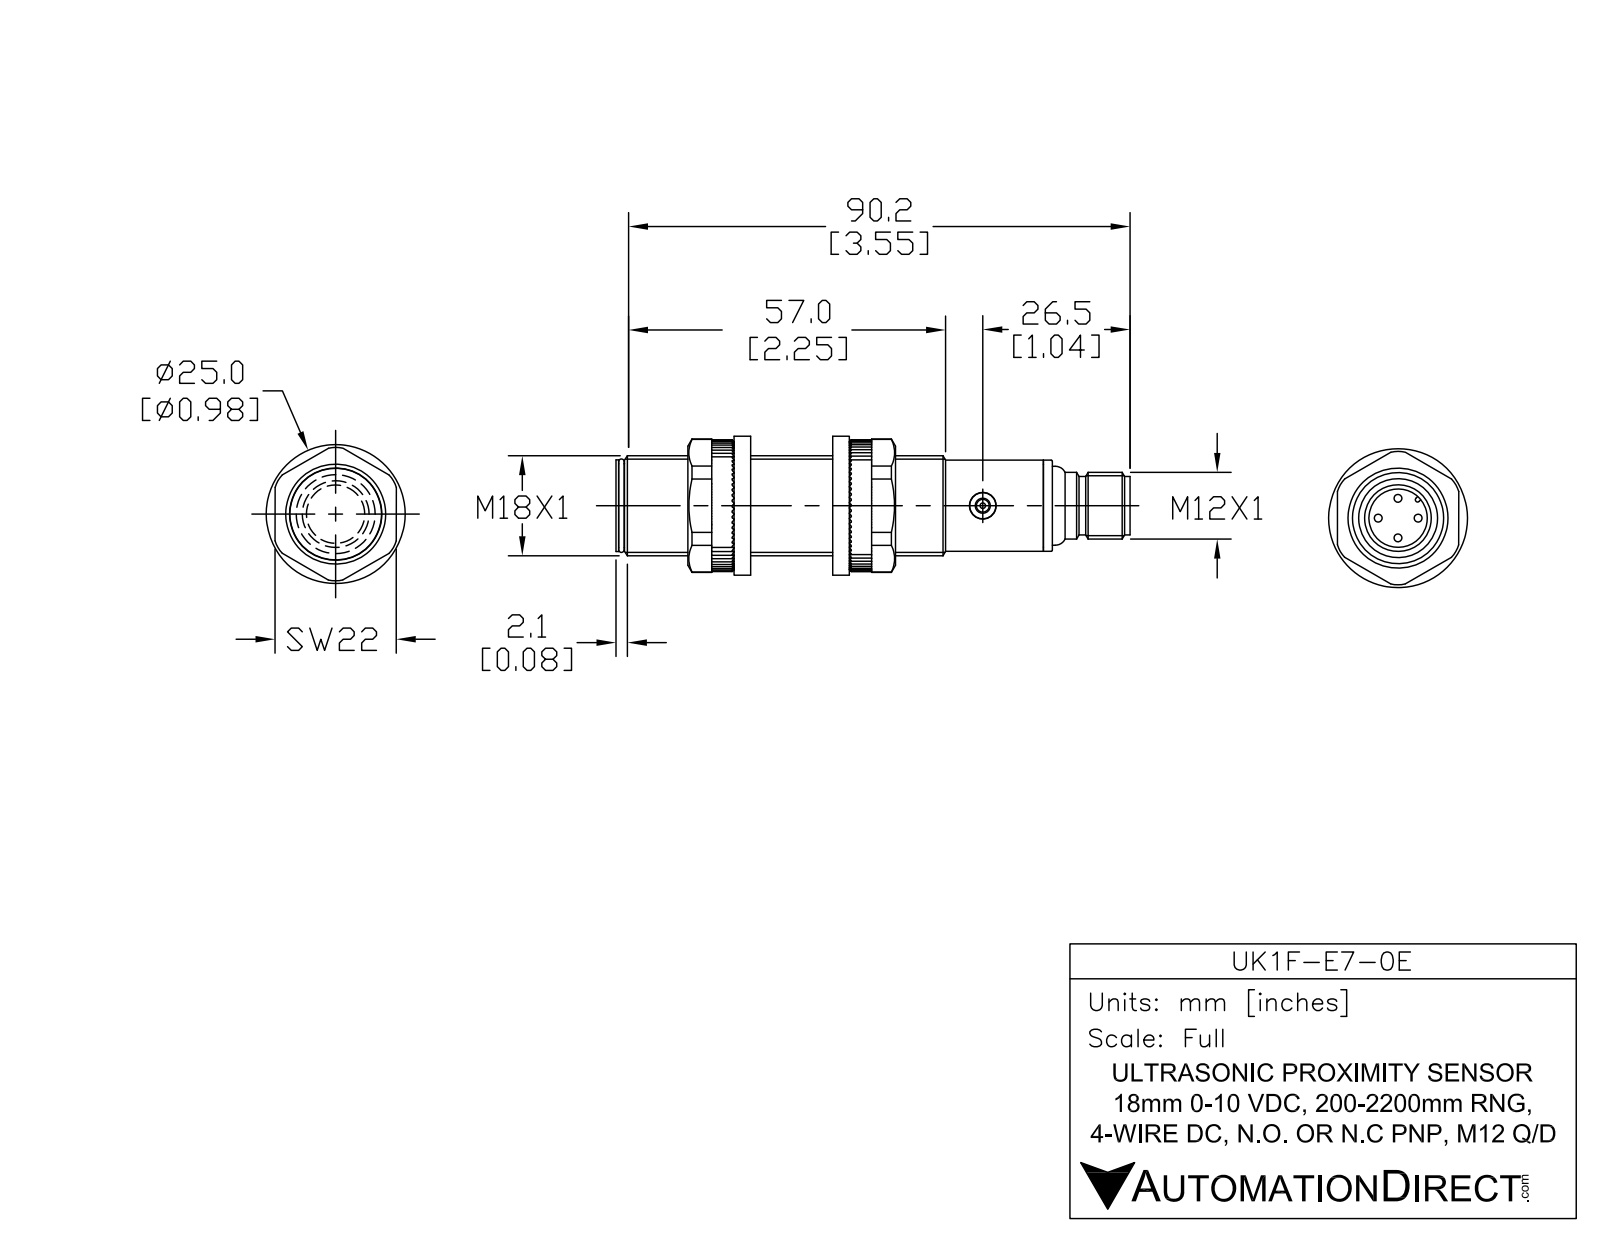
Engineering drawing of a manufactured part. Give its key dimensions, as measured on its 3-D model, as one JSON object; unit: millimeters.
{"part_name": "UK1F-E7-0E", "step_written_by": "SolidWorks 2017 (AUTOMOTIVE_DESIGN)", "units": "millimeters", "bodies": {"solids": 6, "faces": 106, "planar": 21, "cylindrical": 48, "other": 37}, "overall_size": [91.6, 18, 18], "volume_mm3": 19700, "surface_area_mm2": 6890, "round_holes": [[2.7, 1], [4.7, 1], [7, 1], [8.3, 1], [9.5, 1]], "round_bosses_or_shafts": [[1, 4], [18, 1], [16.6, 1], [16.4, 1], [15.8, 1], [14.2, 1], [12, 1], [10.5, 1]], "partial_cylinders_radius": [[0.6, 1]], "face_to_face_distances": [75.1, 1, 76.1, 0.9, 76, 1.1, 4, 77.6, 77.5, 76.6]}
